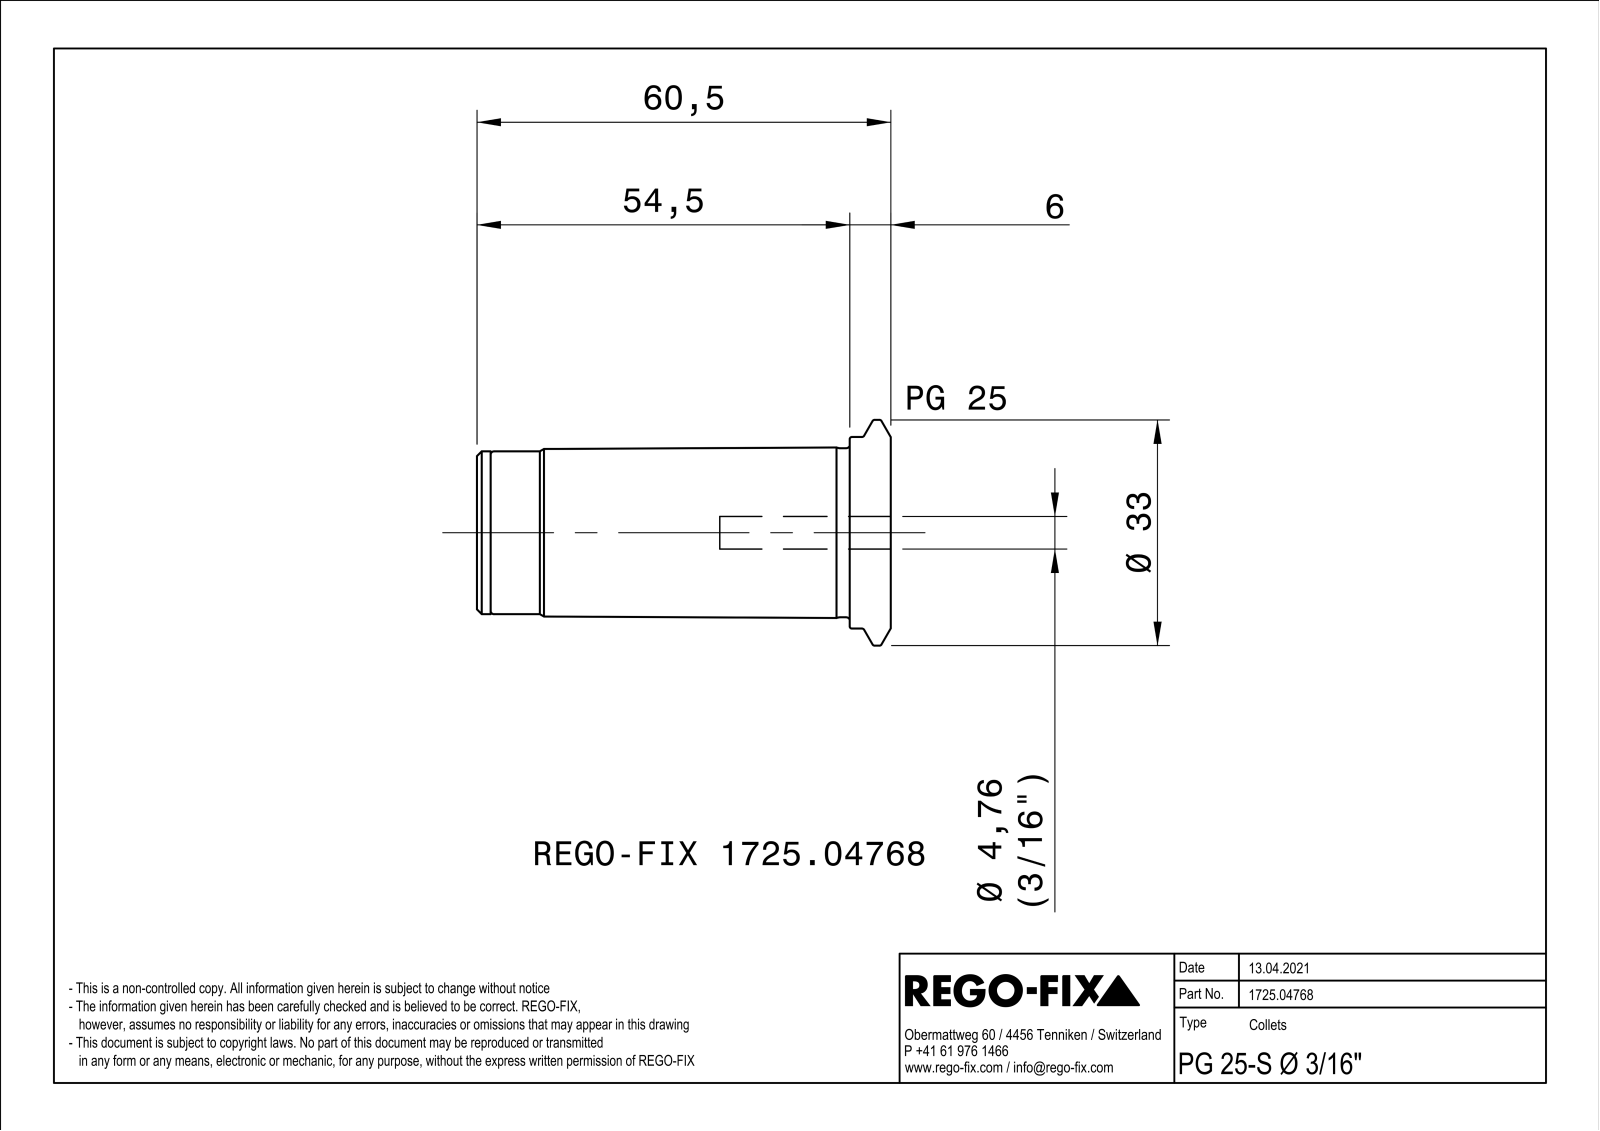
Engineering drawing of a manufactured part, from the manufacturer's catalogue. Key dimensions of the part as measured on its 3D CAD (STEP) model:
Part name (STEP PRODUCT): NOCUT
STEP written by: SIEMENS PLM Software Solid Edge ST10 (AUTOMOTIVE_DESIGN)
Units: millimetres
Bodies: 1 solid, 89 faces (23 planar, 25 cylindrical, 41 other)
Overall size (bounding box): 60.5 × 33 × 32.99
Round holes (diameter × count): ⌀2.5 ×3, ⌀4.76 ×1, ⌀5 ×1, ⌀6.92 ×1, ⌀7.2 ×1, ⌀8.2 ×1, ⌀9 ×1, ⌀20.4 ×1, ⌀20.92 ×1, ⌀22.2 ×1
Round bosses / shafts (diameter × count): ⌀33 ×1, ⌀28 ×1, ⌀24.7 ×1, ⌀23.8 ×1, ⌀12 ×1
Main face-to-face distances: 1, 60.5, 52.6, 7.9, 58.5, 5.9, 2, 6, 52.5, 50
Hole centre spacings: 7.75, 13.43, 13.42
